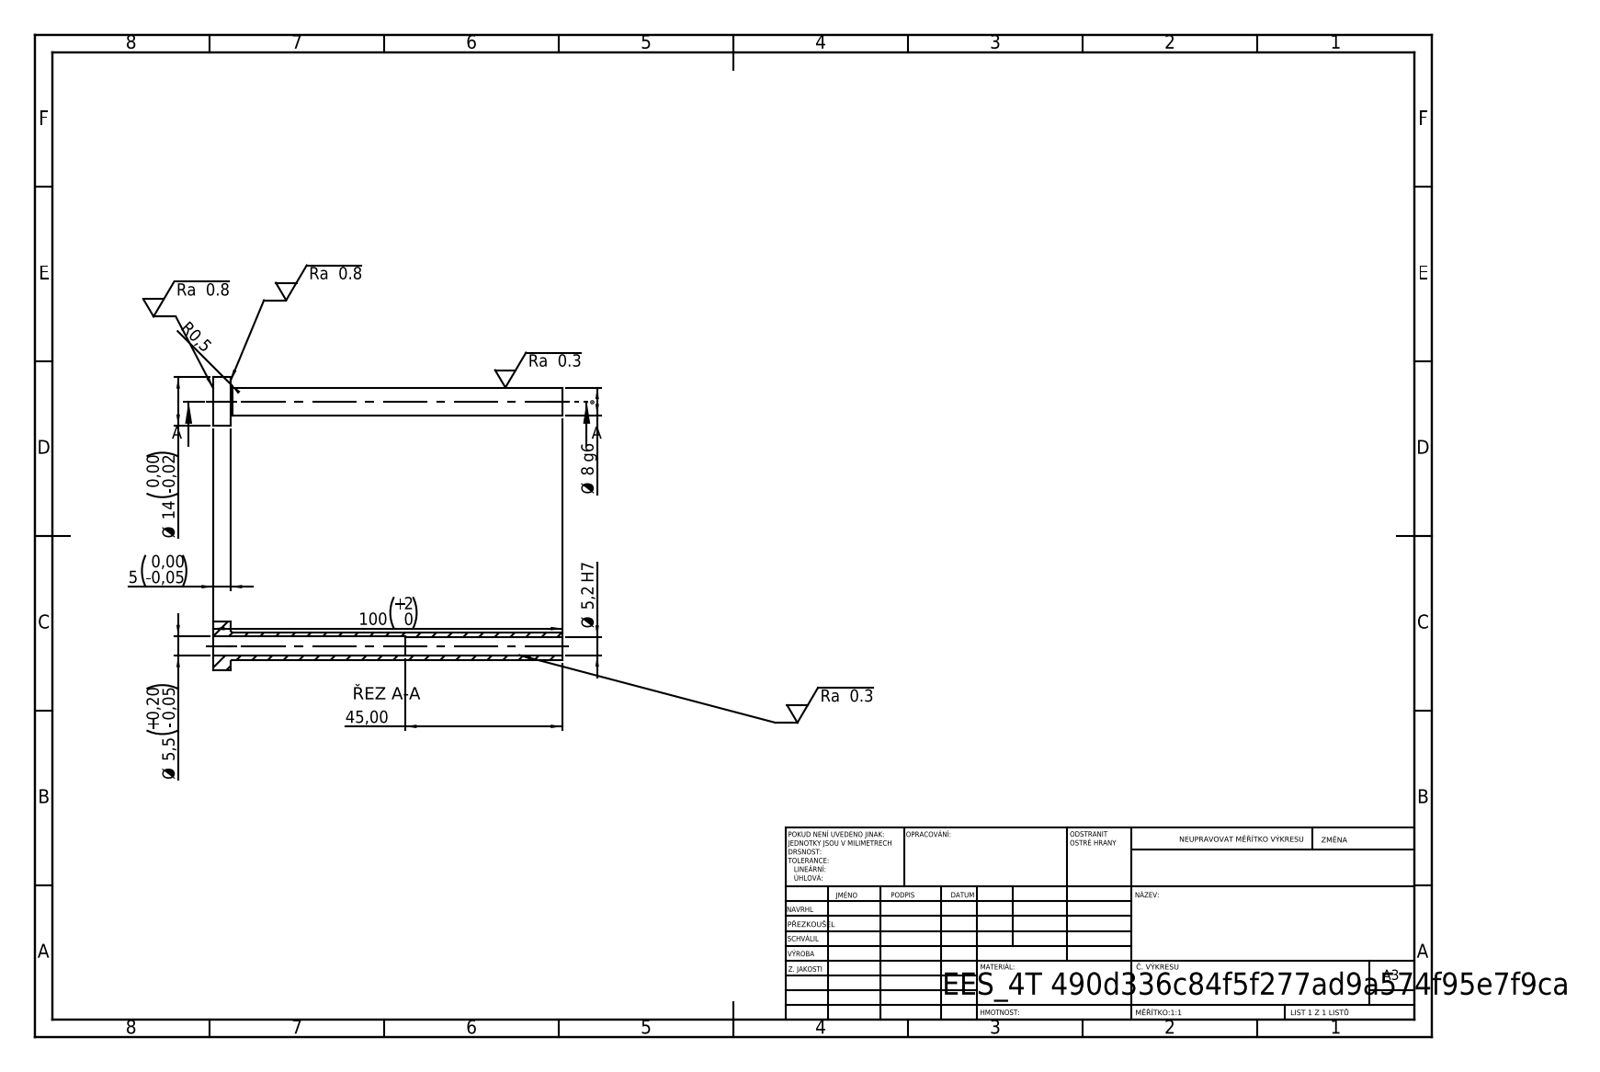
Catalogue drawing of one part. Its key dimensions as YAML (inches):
step_written_by: "SolidWorks 2019 (CONFIG_CONTROL_DESIGN)"
units: inches
bodies: {solids: 1, faces: 14, planar: 4, cylindrical: 8, other: 2}
overall_size: [3.937, 0.551, 0.551]
volume: 0.2
surface_area: 7.057
round_holes:
  - {diameter: 0.205, count: 1}
  - {diameter: 0.217, count: 1}
round_bosses_or_shafts:
  - {diameter: 0.551, count: 1}
  - {diameter: 0.315, count: 1}
face_to_face_distances: [0.197, 3.937, 3.74, 2.165, 1.969, 1.772]
